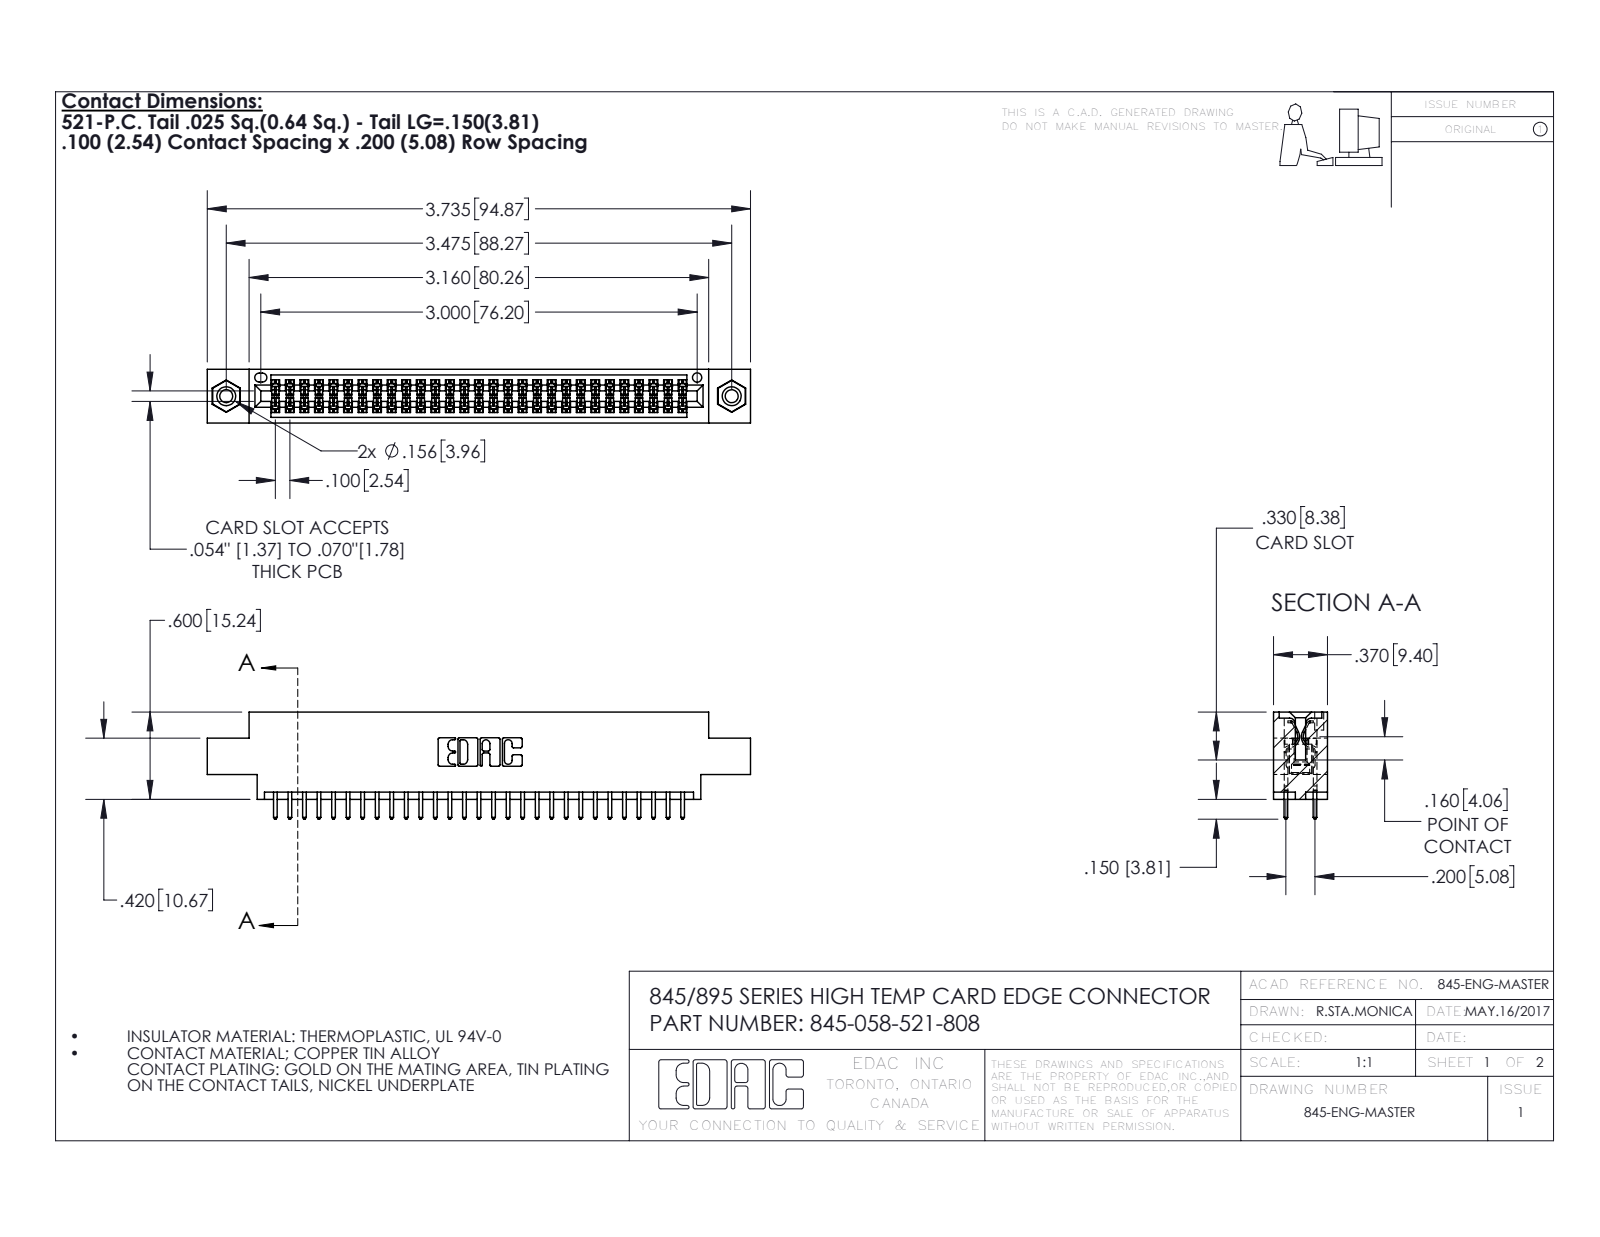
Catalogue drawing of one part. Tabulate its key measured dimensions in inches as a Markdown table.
| quantity | value |
| --- | --- |
| part name | 345-058-521-808; 345 Part_0.170 Offset - 0.156 Dia-TI; 345-250-001_345-250-003-102; 345-292-001_345-293-121 |
| STEP written by | SolidWorks 2016 (CONFIG_CONTROL_DESIGN) |
| units | inches |
| bodies | 61 solids, 3090 faces (2030 planar, 1044 cylindrical, 16 other) |
| overall size | 3.735 × 0.737 × 0.37 |
| volume | 0.546 in³ |
| surface area | 20.12 in² |
| round holes (diameter × count) | 0.089 × 2, 0.125 × 2, 0.156 × 2, 0.064 × 1 |
| round bosses / shafts (diameter × count) | 0.155 × 2 |
| partial cylindrical surfaces (radius × count) | 0.006 × 87, 0.01 × 58, 0.01 × 22, 0.007 × 6, 0.031 × 6, 0.026 × 3, 0.014 × 2, 0.019 × 2 |
| main face-to-face distances | 0.072, 0.298, 0.37, 0.2, 0.098, 0.272, 0.025, 0.225, 0.175, 0.149 |
| hole center spacings | 0.27, 3.24, 3.475 |
